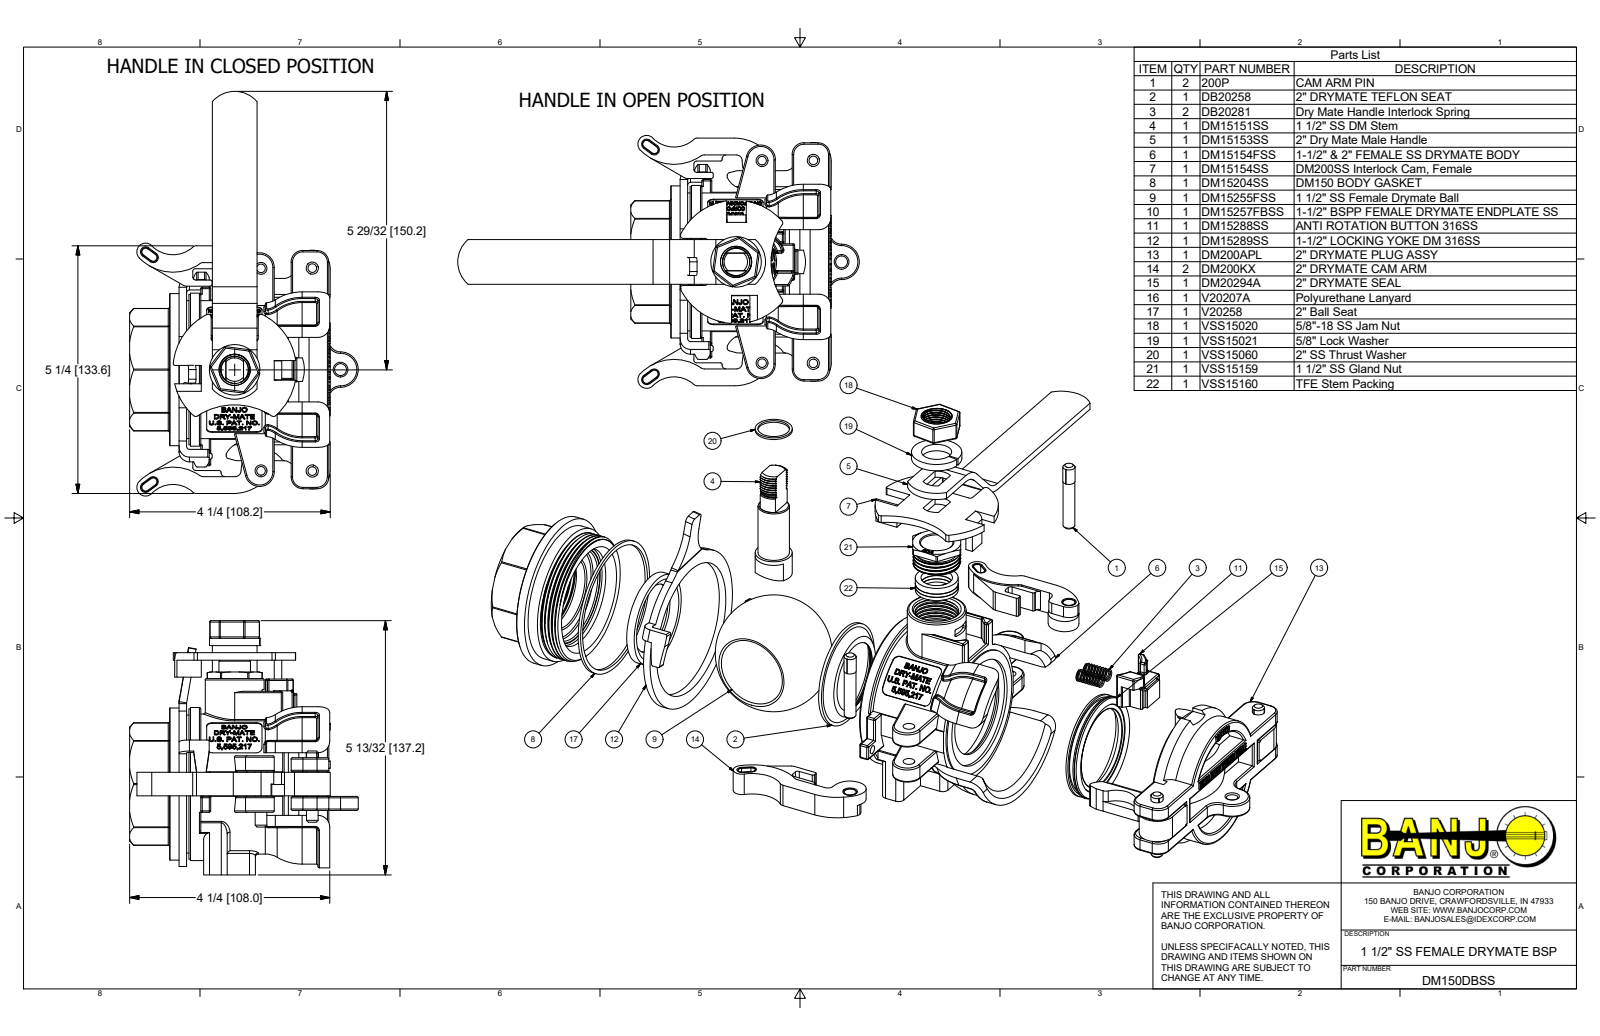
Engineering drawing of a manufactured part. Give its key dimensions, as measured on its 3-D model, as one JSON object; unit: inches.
{"part_name": "DM150DBSS; DM15154FSS; DB20258; DB20281 (+8 more)", "step_written_by": "Autodesk Inventor 2017 (AUTOMOTIVE_DESIGN)", "units": "inches", "bodies": {"solids": 35, "faces": 2810, "planar": 1146, "cylindrical": 640, "other": 1024}, "overall_size": [13.635, 5.915, 5.406], "volume_in3": 29.11, "surface_area_in2": 336.5, "round_holes": [[0.25, 5], [0.256, 4], [0.125, 3], [1.5, 2], [0.18, 1], [0.58, 1], [0.64, 1], [0.662, 1], [0.67, 1], [0.676, 1], [0.69, 1], [0.84, 1]], "round_bosses_or_shafts": [[0.26, 4], [0.249, 4], [0.28, 3], [3.5, 1], [3.23, 1], [3.19, 1], [2.975, 1], [2.97, 1]], "partial_cylinders_radius": [[0.03, 175], [0.06, 25], [0.125, 14], [0.12, 10], [0.25, 10], [0.08, 9], [0.032, 6], [1, 6]], "face_to_face_distances": [0.298, 0.16, 0.15, 1.68, 2.18, 0.85, 0.86, 0.86, 0.31, 0.81], "hole_center_spacings": [0.95, 1.09, 1.646, 2.222, 2.237, 2.249, 2.713, 2.735]}
